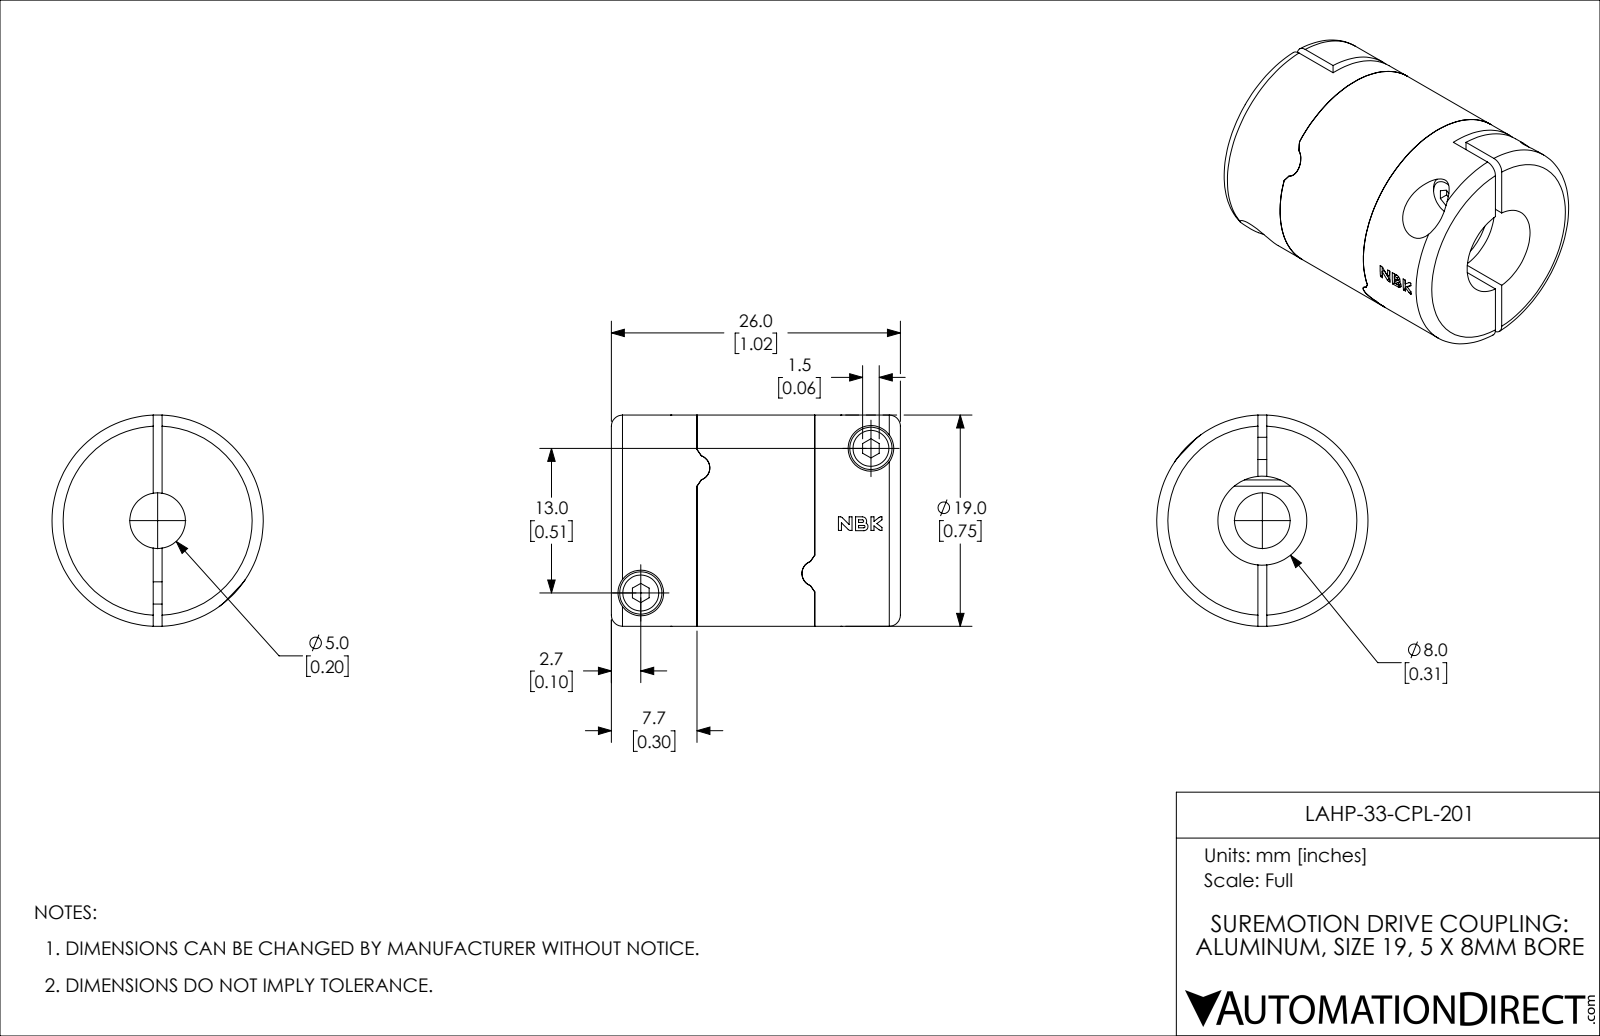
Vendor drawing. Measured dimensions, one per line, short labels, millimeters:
name: LAHP-33-CPL-201
written by: SolidWorks 2019 (CONFIG_CONTROL_DESIGN)
unit: mm
bodies: 3 solids, 162 faces (92 planar, 56 cylindrical, 14 other)
size: 26 × 19 × 19
volume: 5 770 mm³; area: 4 466 mm²
holes: 2× ⌀2, 2× ⌀2.5, 2× ⌀4.1, 1× ⌀5, 1× ⌀8, 1× ⌀8.8
bosses: 2× ⌀3.8, 1× ⌀19
rounds: 4× R0.3, 2× R1.1, 1× R0.1, 1× R0.1, 1× R0.4, 1× R0.4
face distances: 7.7, 18.3, 10.6, 0.8, 5.4, 20.7, 2.4, 13, 4.5, 21.4
hole spacings: 24.4
